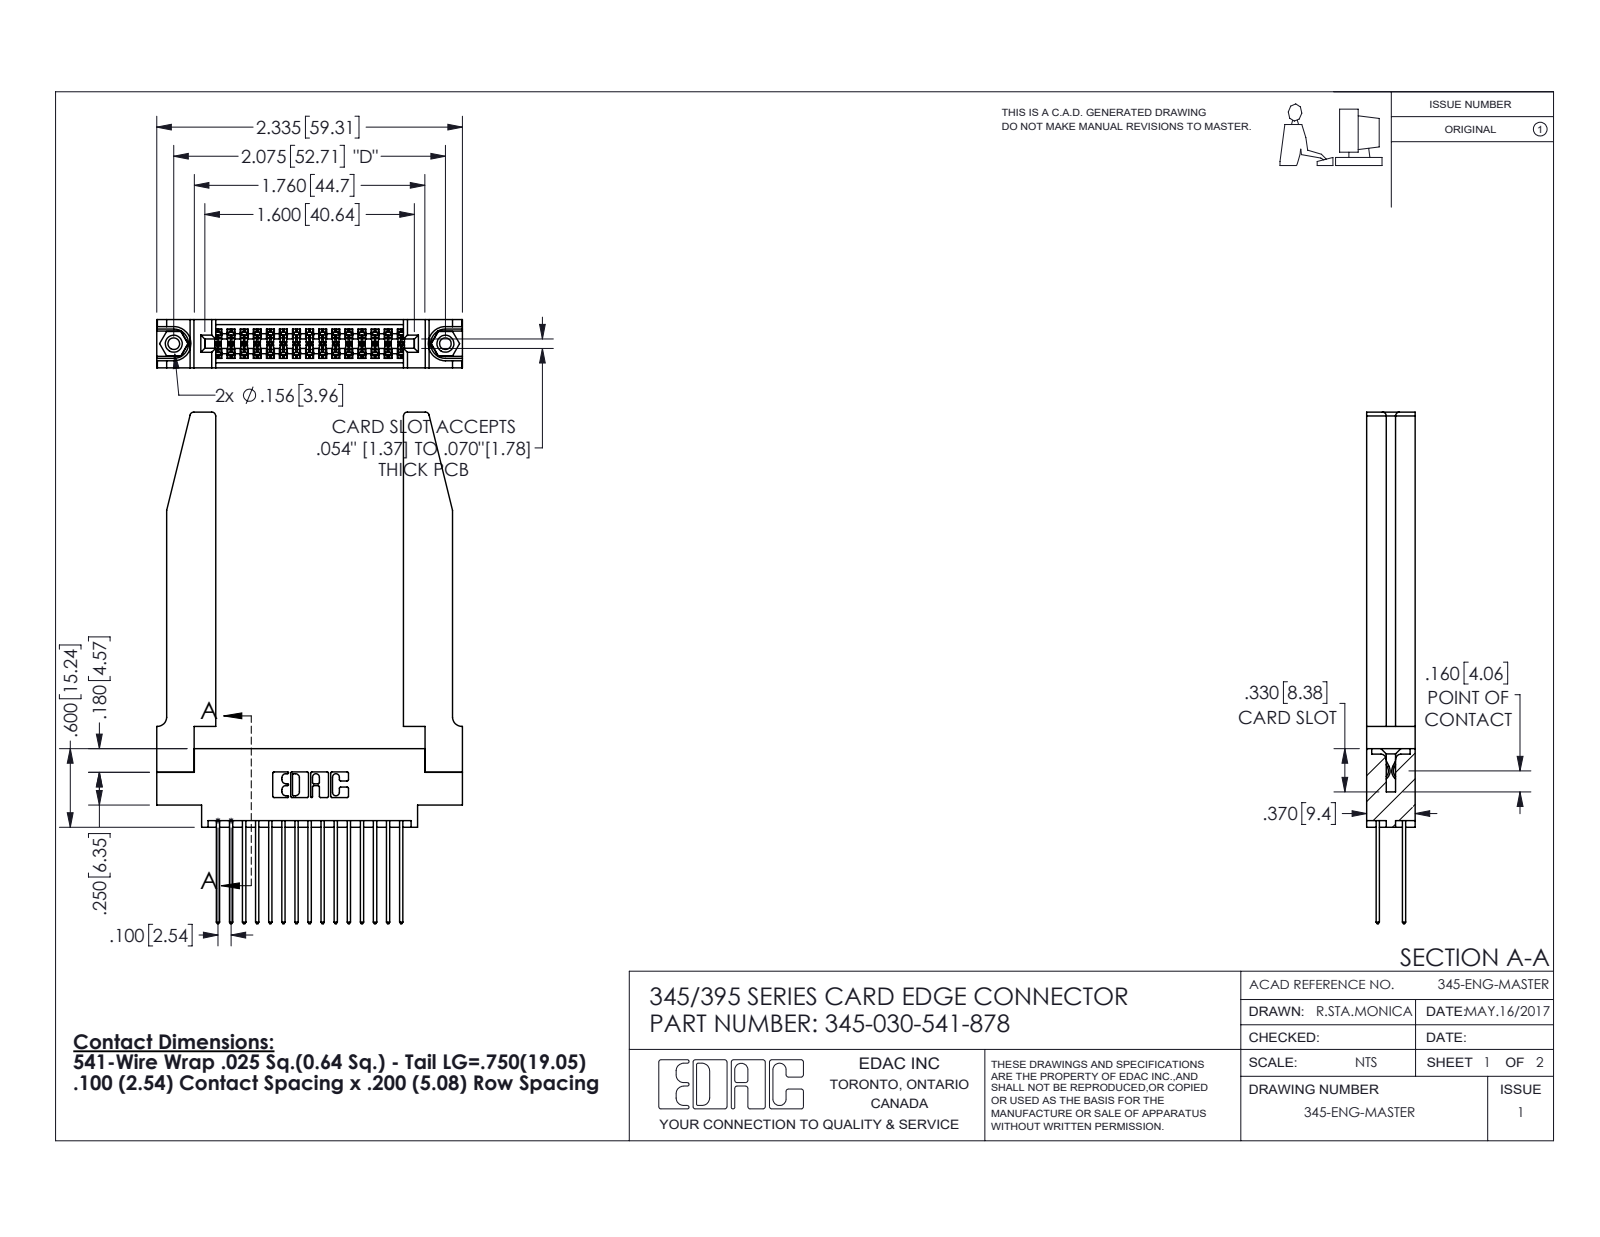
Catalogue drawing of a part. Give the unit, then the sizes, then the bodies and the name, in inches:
Units: inches
Overall size (bounding box): 3.907 × 2.336 × 0.37
Round holes (diameter × count): ⌀0.089 ×2, ⌀0.125 ×2, ⌀0.156 ×2, ⌀0.064 ×1
Round bosses / shafts (diameter × count): ⌀0.155 ×2
Partial cylindrical surfaces — rounded edges, fillets, slot ends (radius × count): R0.006 ×45, R0.01 ×30, R0.01 ×22, R0.03 ×8, R0.007 ×6, R0.031 ×6, R0.026 ×3, R0.014 ×2
Main face-to-face distances: 0.37, 0.072, 0.298, 0.098, 0.272, 0.025, 0.2, 0.225, 0.15, 0.148
Hole centre spacings: 0.27, 1.842, 2.075
Volume: 0.814 in³ · Surface area: 24.03 in²
Bodies: 35 solids, 1864 faces (1216 planar, 596 cylindrical, 52 other)
Part name (STEP PRODUCT): 345-250-001_345-250-001-102; 345-292-001_345-293-141; 345-220-078_345-220-078; 345 Part_0.170 Offset - 0.156 Dia-TH (+1 more)
STEP written by: SolidWorks 2016 (CONFIG_CONTROL_DESIGN)
